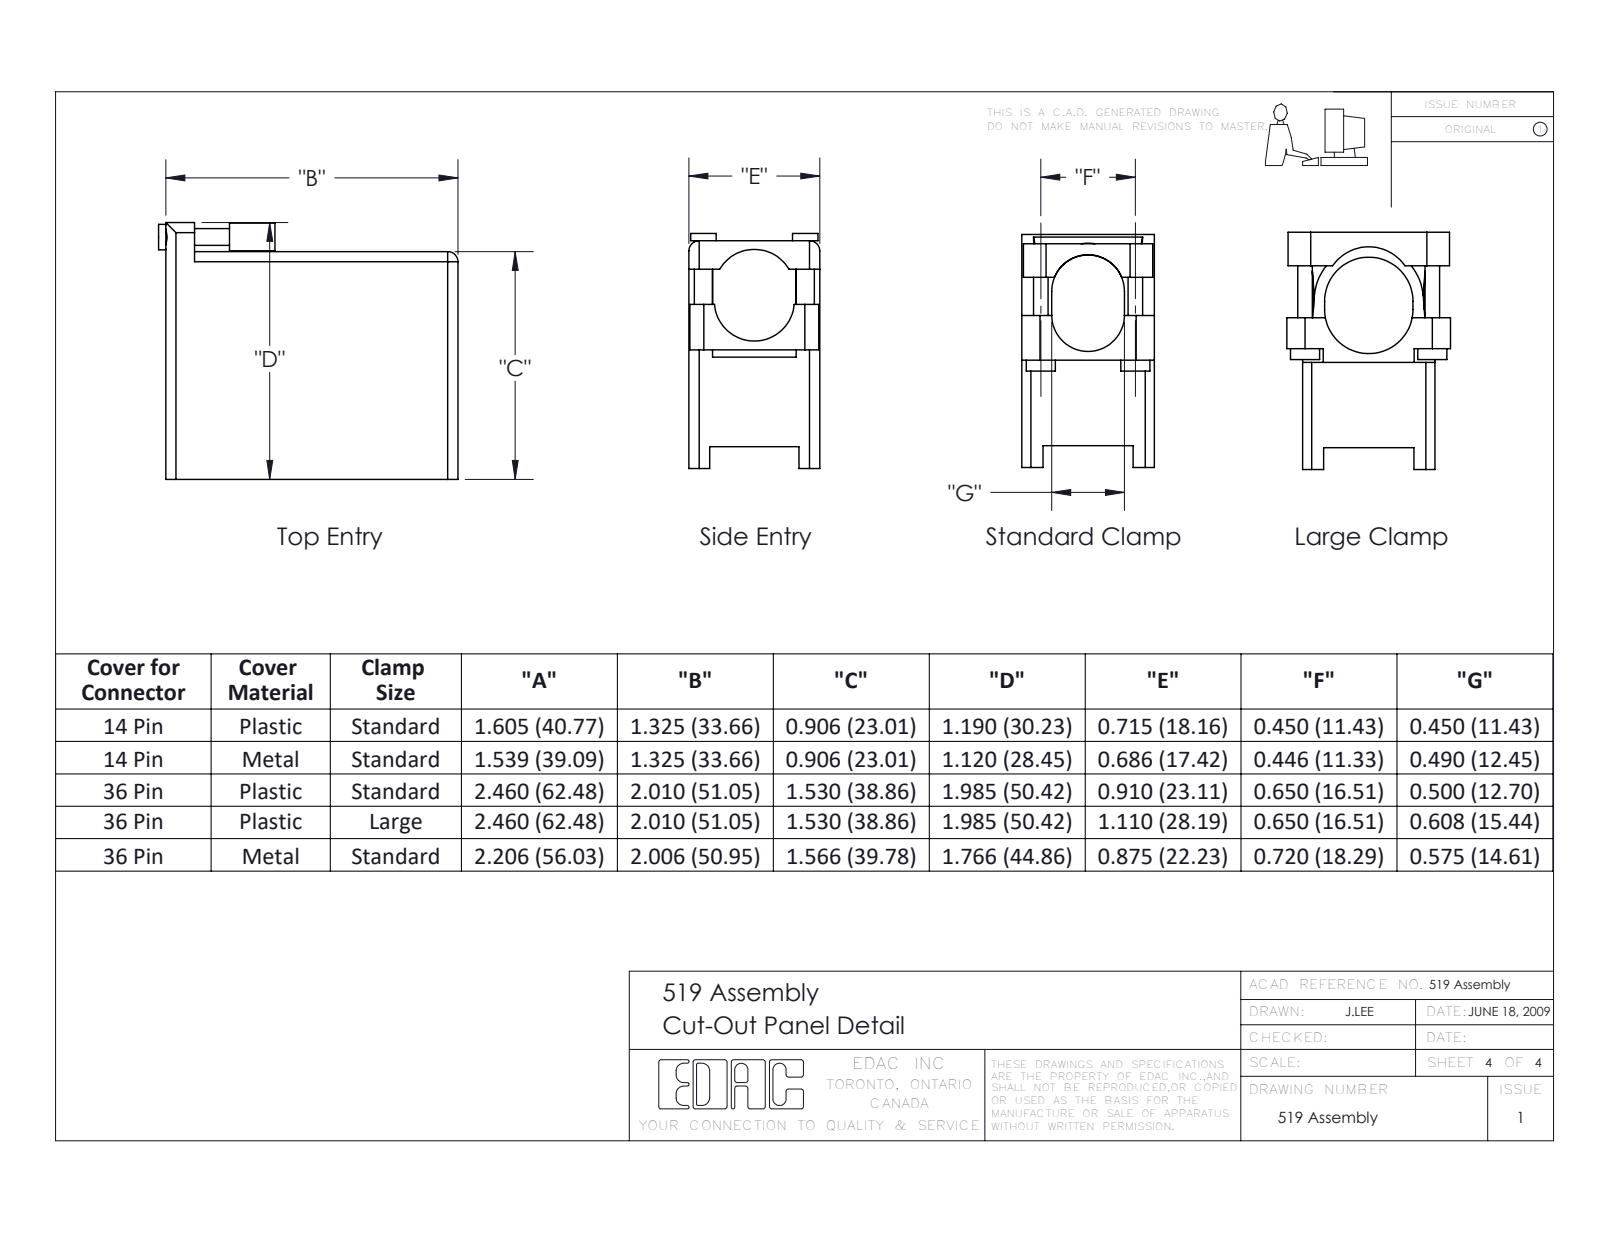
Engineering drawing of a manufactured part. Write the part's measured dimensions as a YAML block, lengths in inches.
part_name: "516-222-038-102_039; 516-292-001_520 Contact; 516-252-035-100_516-252-035-100; 516-252-021-102_038 (+3 more)"
step_written_by: "SolidWorks 2016 (CONFIG_CONTROL_DESIGN)"
units: inches
bodies: {solids: 42, faces: 3684, planar: 2182, cylindrical: 1194, other: 308}
overall_size: [2, 1.142, 0.876]
volume: 0.657
surface_area: 28.65
round_holes:
  - {diameter: 0.13, count: 37}
  - {diameter: 0.05, count: 17}
  - {diameter: 0.12, count: 6}
  - {diameter: 0.19, count: 4}
  - {diameter: 0.089, count: 2}
  - {diameter: 0.26, count: 2}
  - {diameter: 0.101, count: 1}
  - {diameter: 0.163, count: 1}
  - {diameter: 0.206, count: 1}
  - {diameter: 0.296, count: 1}
round_bosses_or_shafts:
  - {diameter: 0.25, count: 2}
  - {diameter: 0.112, count: 2}
  - {diameter: 0.08, count: 2}
  - {diameter: 0.203, count: 1}
  - {diameter: 0.11, count: 1}
  - {diameter: 0.09, count: 1}
partial_cylinders:
  - {radius: 0.022, count: 108}
  - {radius: 0.012, count: 82}
  - {radius: 0.008, count: 72}
  - {radius: 0.016, count: 72}
  - {radius: 0.08, count: 42}
  - {radius: 0.007, count: 34}
  - {radius: 0.01, count: 22}
  - {radius: 0.013, count: 17}
face_to_face_distances: [0.212, 0.106, 0.318, 0.53, 0.024, 0.106, 0.636, 0.424, 0.188, 0.424]
hole_center_spacings: [0.212, 0.15, 0.335, 0.424, 0.3, 0.106, 0.318, 0.53]
